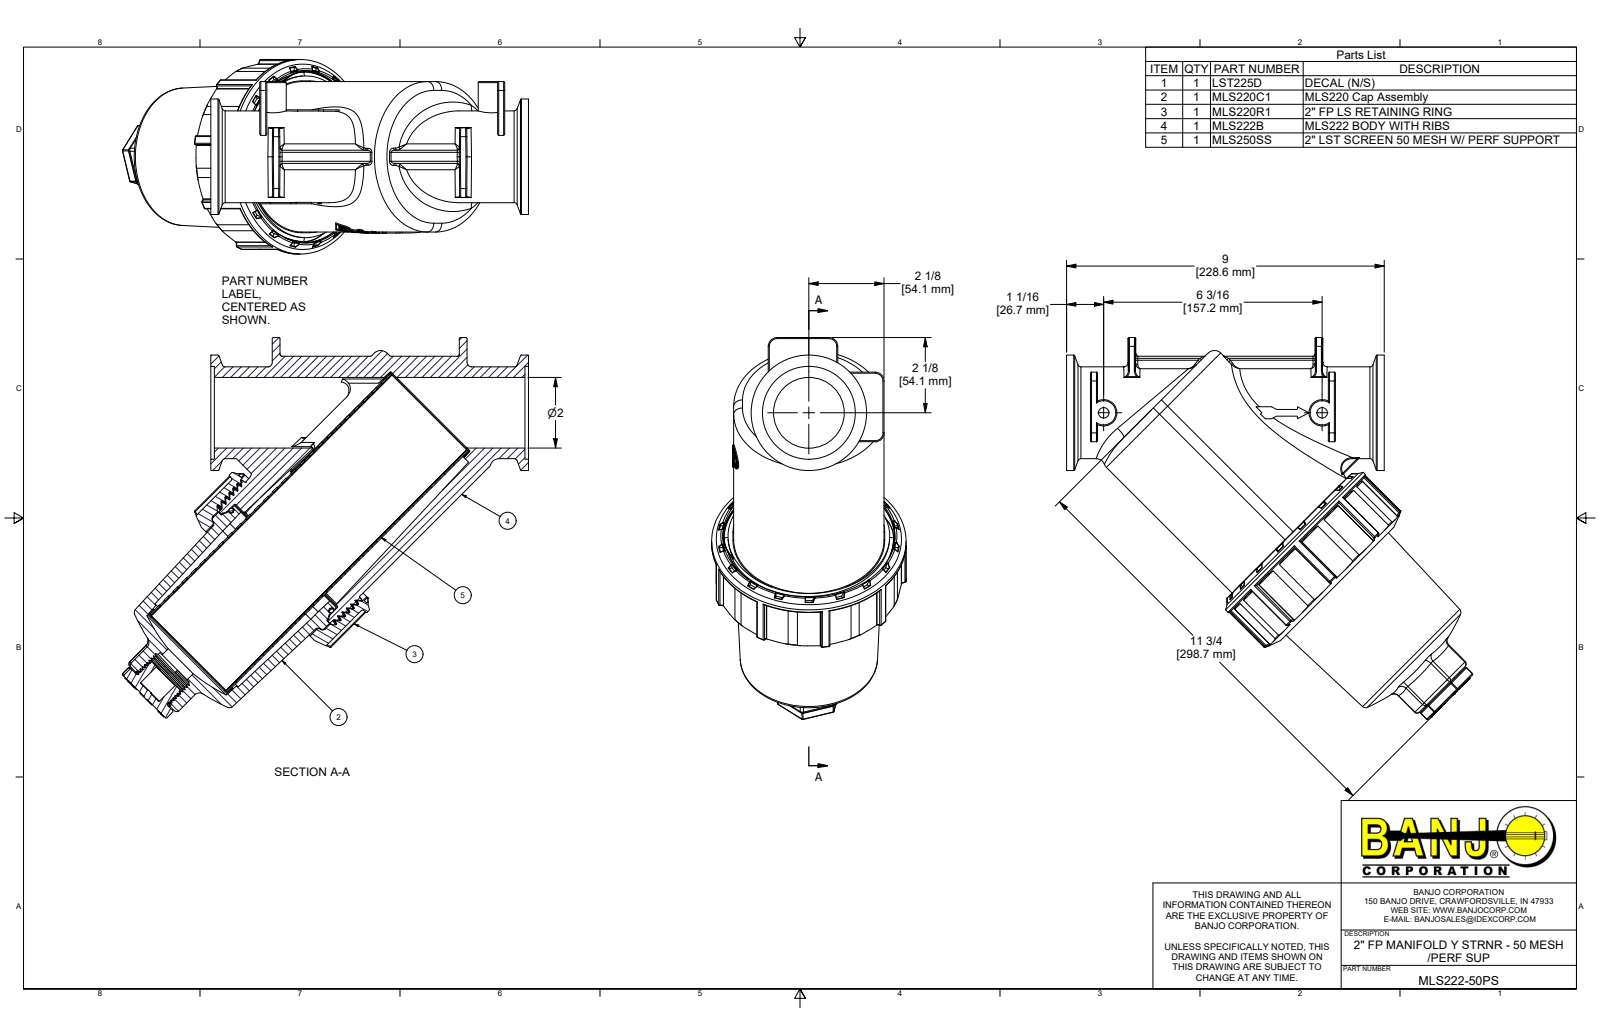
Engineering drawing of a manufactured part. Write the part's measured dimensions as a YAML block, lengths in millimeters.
part_name: "MLS222-50PS; MLS222B; MLS220C1; MLS220C1X (+5 more)"
step_written_by: "Autodesk Inventor 2019 (AUTOMOTIVE_DESIGN)"
units: millimeters
bodies: {solids: 10, faces: 2668, planar: 786, cylindrical: 1101, other: 781}
overall_size: [292.3, 274.8, 140]
volume: 1389000
surface_area: 568900
round_holes:
  - {diameter: 6.4, count: 723}
  - {diameter: 7.5, count: 2}
  - {diameter: 74.6, count: 2}
  - {diameter: 79.5, count: 2}
  - {diameter: 11.5, count: 1}
  - {diameter: 16.3, count: 1}
  - {diameter: 19.1, count: 1}
  - {diameter: 25.4, count: 1}
  - {diameter: 29.9, count: 1}
  - {diameter: 50.8, count: 1}
  - {diameter: 66.8, count: 1}
  - {diameter: 75.9, count: 1}
round_bosses_or_shafts:
  - {diameter: 81, count: 2}
  - {diameter: 140, count: 1}
  - {diameter: 133.4, count: 1}
  - {diameter: 113, count: 1}
  - {diameter: 107.1, count: 1}
  - {diameter: 104.1, count: 1}
  - {diameter: 99.2, count: 1}
  - {diameter: 83.1, count: 1}
partial_cylinders:
  - {radius: 0.8, count: 76}
  - {radius: 0.3, count: 36}
  - {radius: 1.5, count: 12}
  - {radius: 2.3, count: 12}
  - {radius: 6.4, count: 8}
  - {radius: 3.2, count: 6}
  - {radius: 0.5, count: 2}
  - {radius: 1, count: 2}
face_to_face_distances: [2.5, 226.1, 7.6, 228.6, 147.5, 155.2, 134.6, 0.8, 5.1, 171.2]
hole_center_spacings: [9.2, 36.8, 18.4, 64.4, 82.9, 27.6, 55.2, 110.5]
